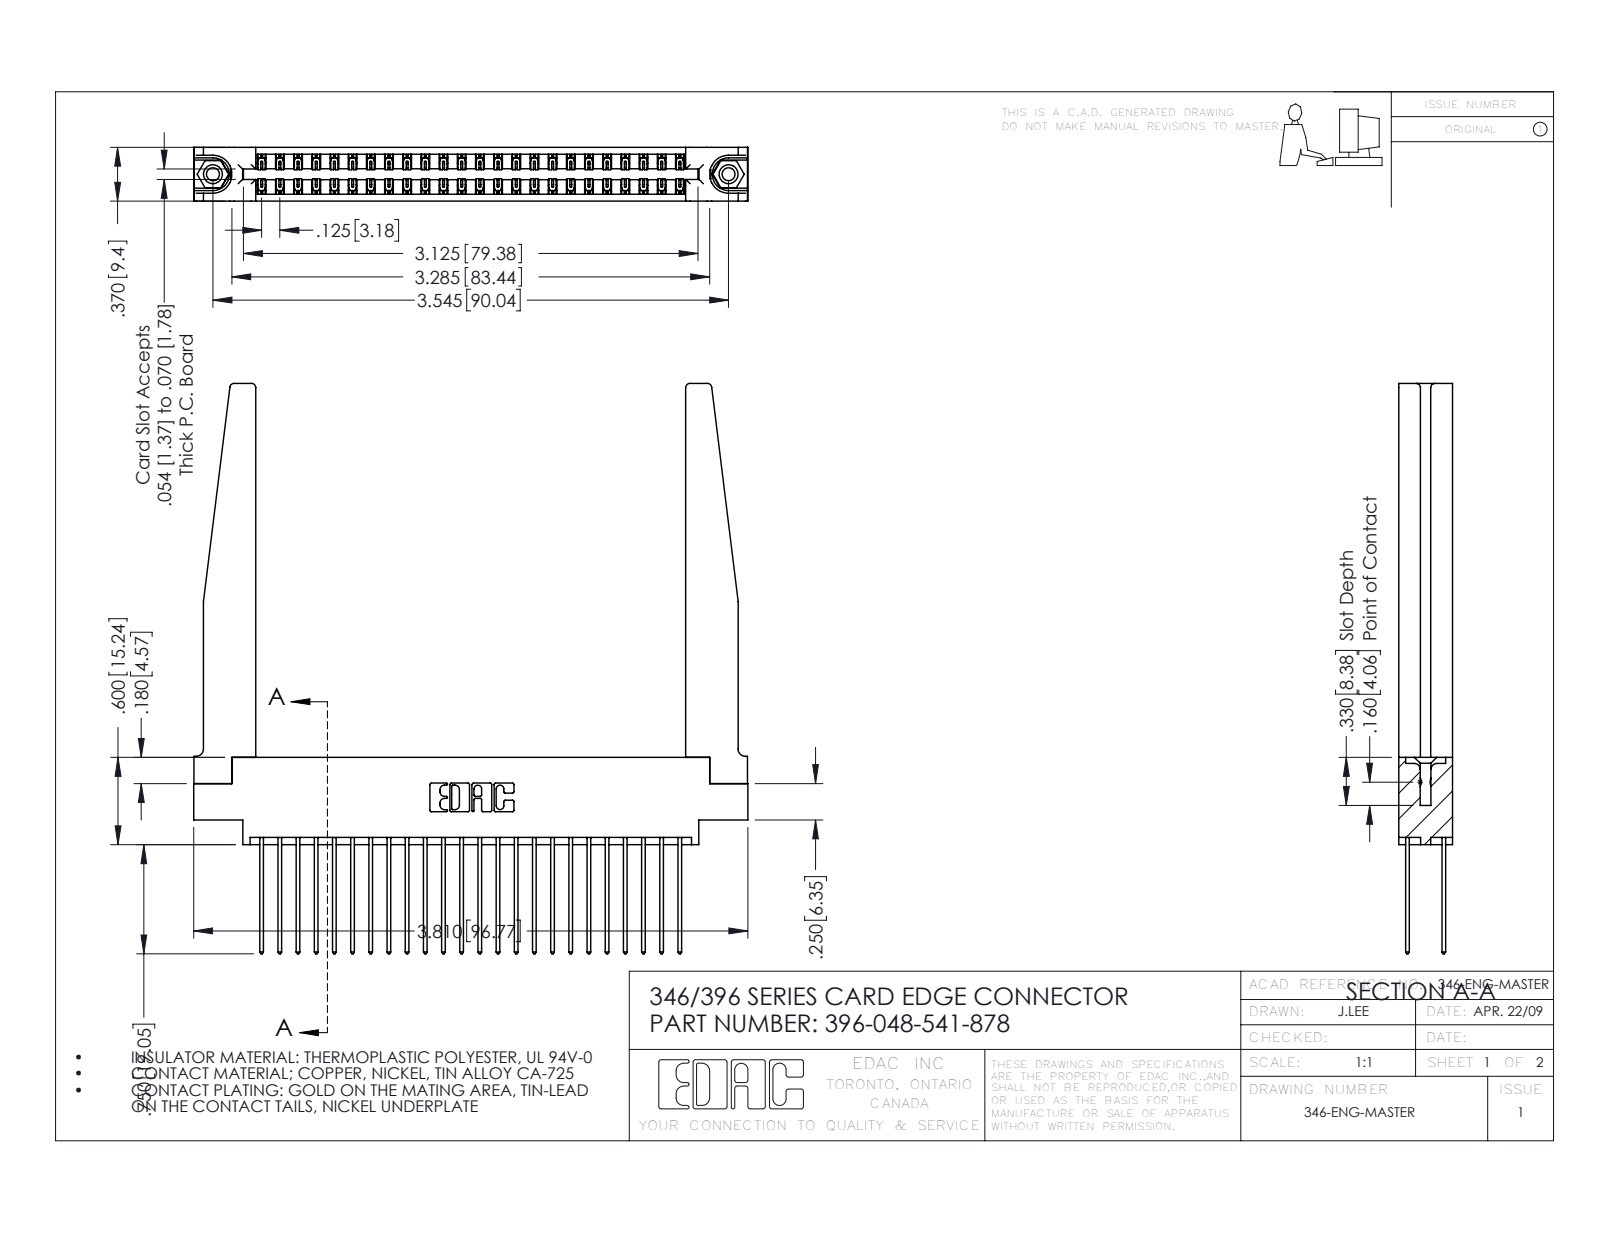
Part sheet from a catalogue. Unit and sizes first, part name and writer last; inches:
Units: inches
Overall size (bounding box): 3.92 × 3.81 × 0.37
Round holes (diameter × count): ⌀0.089 ×2, ⌀0.125 ×2, ⌀0.156 ×2, ⌀0.064 ×1
Round bosses / shafts (diameter × count): ⌀0.155 ×2
Partial cylindrical surfaces — rounded edges, fillets, slot ends (radius × count): R0.006 ×72, R0.01 ×48, R0.01 ×22, R0.03 ×8, R0.007 ×6, R0.031 ×6, R0.026 ×3, R0.014 ×2
Main face-to-face distances: 0.37, 0.048, 0.322, 0.072, 0.25, 0.298, 0.025, 0.148, 0.15, 0.275
Hole centre spacings: 0.246, 3.337, 3.545
Volume: 0.996 in³ · Surface area: 32.09 in²
Bodies: 53 solids, 2856 faces (1902 planar, 902 cylindrical, 52 other)
Part name (STEP PRODUCT): 396-048-541-878; 345-250-001_345-250-001-102; 345-292-001_345-293-141; 346 Part_0.170 Offset - 0.156 Dia-TH (+1 more)
STEP written by: SolidWorks 2016 (CONFIG_CONTROL_DESIGN)
